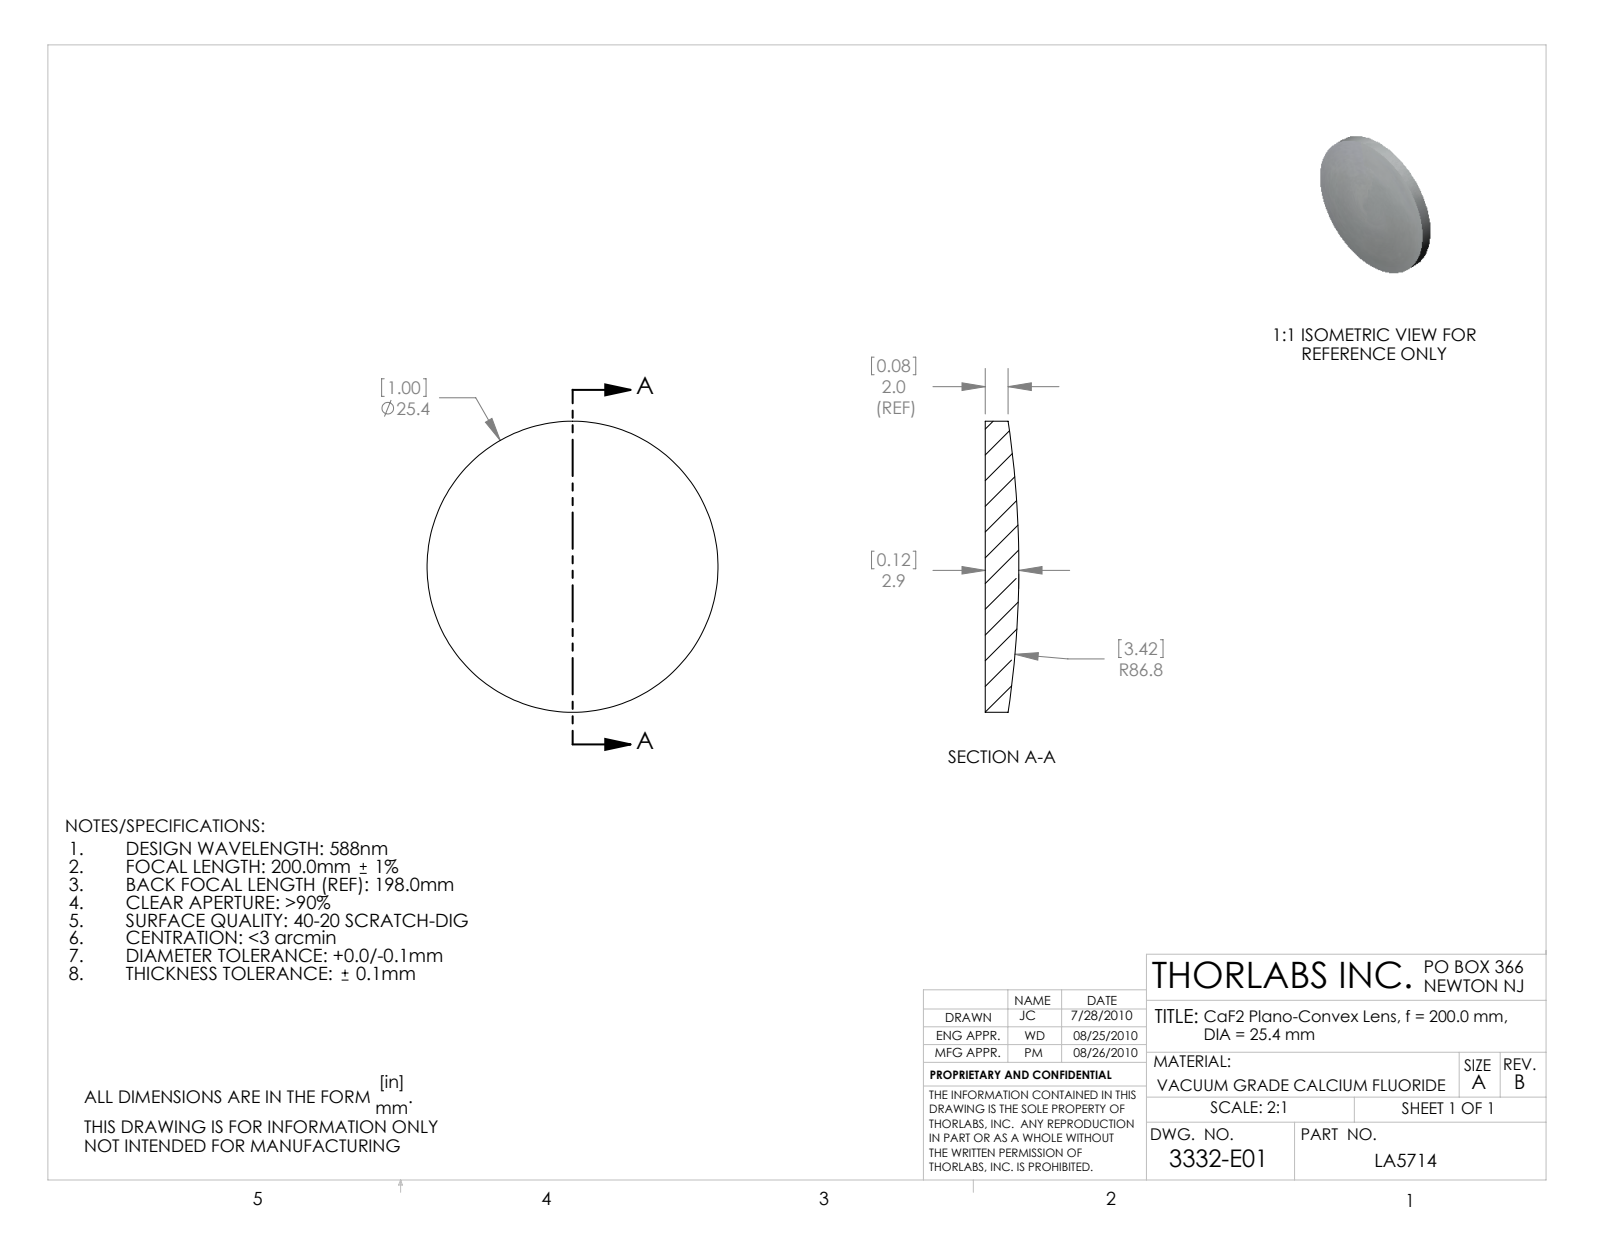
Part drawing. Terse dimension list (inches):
name: 3332-E0W
written by: SolidWorks 2009 (AUTOMOTIVE_DESIGN)
unit: in
bodies: 1 solid, 5 faces (1 planar, 2 cylindrical, 2 other)
size: 1 × 1 × 0.115
volume: 0.076 in³; area: 1.822 in²
bosses: 1× ⌀1
